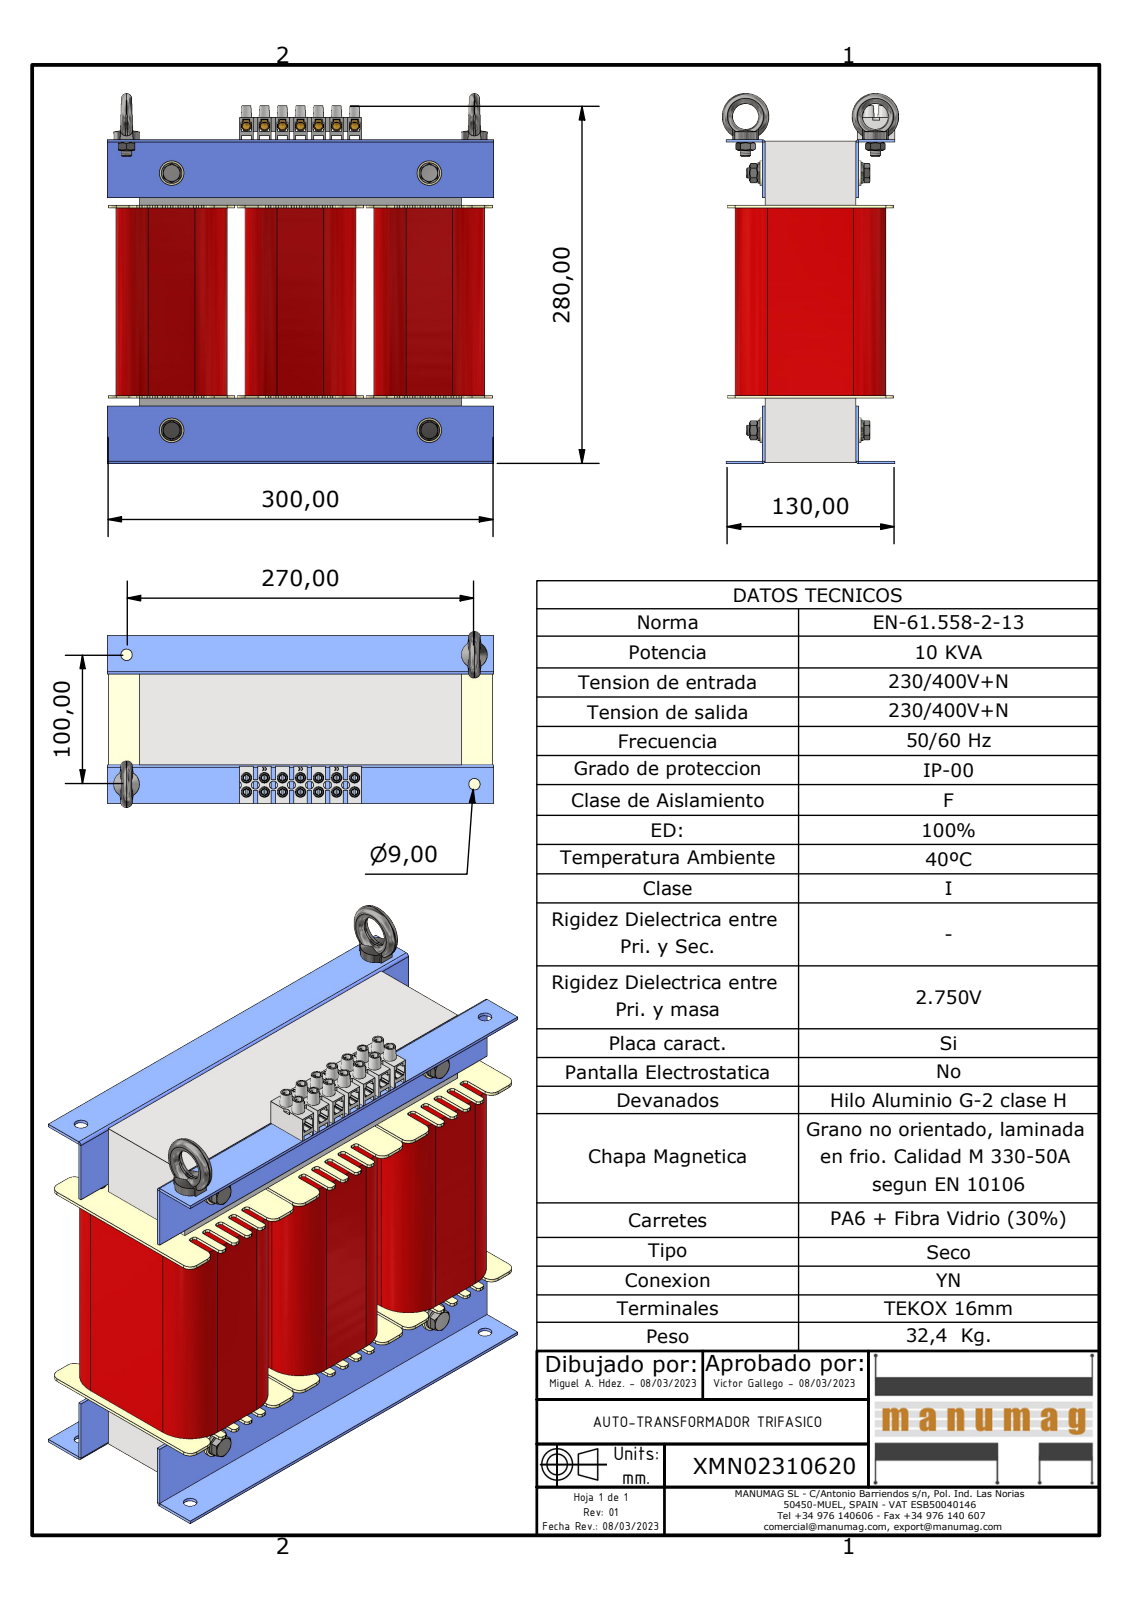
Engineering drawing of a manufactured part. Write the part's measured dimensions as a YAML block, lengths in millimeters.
part_name: "XMN02310620; 3UI150 250 x 250 - 70 (Rc50); UI 150_70; RC50 NT050 (+8 more)"
step_written_by: "Autodesk Inventor 2023 (AUTOMOTIVE_DESIGN)"
units: millimeters
bodies: {solids: 72, faces: 3329, planar: 2225, cylindrical: 619, other: 485}
overall_size: [300, 288, 136]
volume: 6225000
surface_area: 827801
round_holes:
  - {diameter: 3.24, count: 14}
  - {diameter: 5.5, count: 14}
  - {diameter: 6, count: 7}
  - {diameter: 6.3, count: 6}
  - {diameter: 6.65, count: 6}
  - {diameter: 11, count: 6}
  - {diameter: 8, count: 4}
  - {diameter: 8.4, count: 4}
  - {diameter: 9, count: 4}
  - {diameter: 10.5, count: 4}
  - {diameter: 20, count: 2}
round_bosses_or_shafts:
  - {diameter: 4, count: 14}
  - {diameter: 19, count: 4}
  - {diameter: 16, count: 4}
  - {diameter: 11.4, count: 4}
  - {diameter: 9.6, count: 4}
  - {diameter: 7.32, count: 4}
  - {diameter: 36, count: 2}
  - {diameter: 8, count: 2}
partial_cylinders:
  - {radius: 2, count: 108}
  - {radius: 2.75, count: 28}
  - {radius: 6, count: 24}
  - {radius: 0.82, count: 16}
  - {radius: 3, count: 14}
  - {radius: 25, count: 12}
  - {radius: 0.22, count: 9}
  - {radius: 0.81, count: 8}
face_to_face_distances: [50, 100, 2, 200, 70, 150, 250, 1, 51, 199]
hole_center_spacings: [14, 28, 42, 8.8, 9, 17.8, 56, 21.67]
